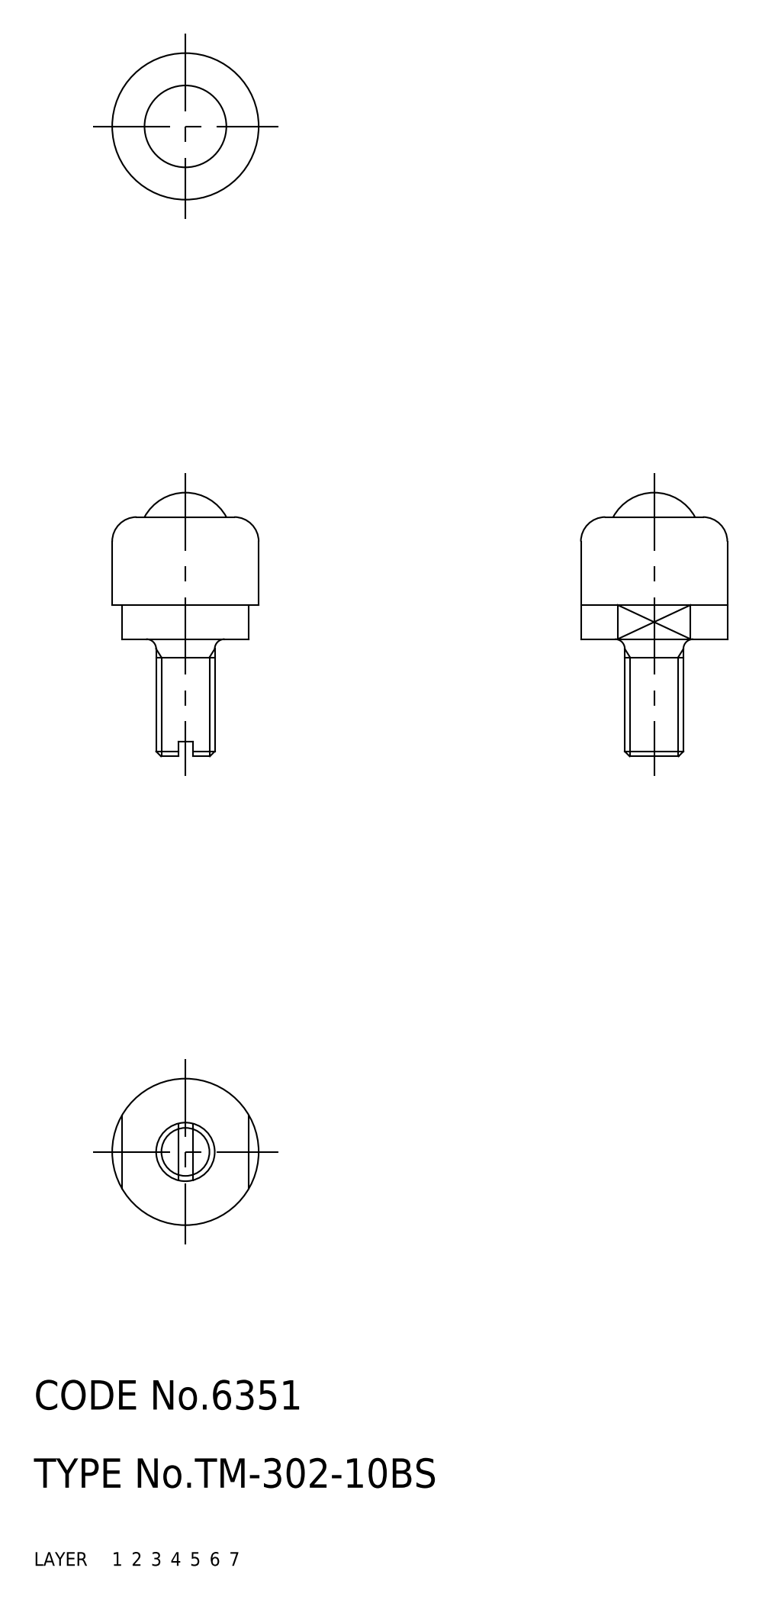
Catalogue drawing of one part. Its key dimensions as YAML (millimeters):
part_name: "67111063; 67111076; 67111089"
step_written_by: "CADfix (AUTOMOTIVE_DESIGN)"
units: millimeters
bodies: {solids: 3, faces: 32, planar: 0, cylindrical: 0, other: 32}
overall_size: [27, 15, 15]
volume: 1675
surface_area: 1945
